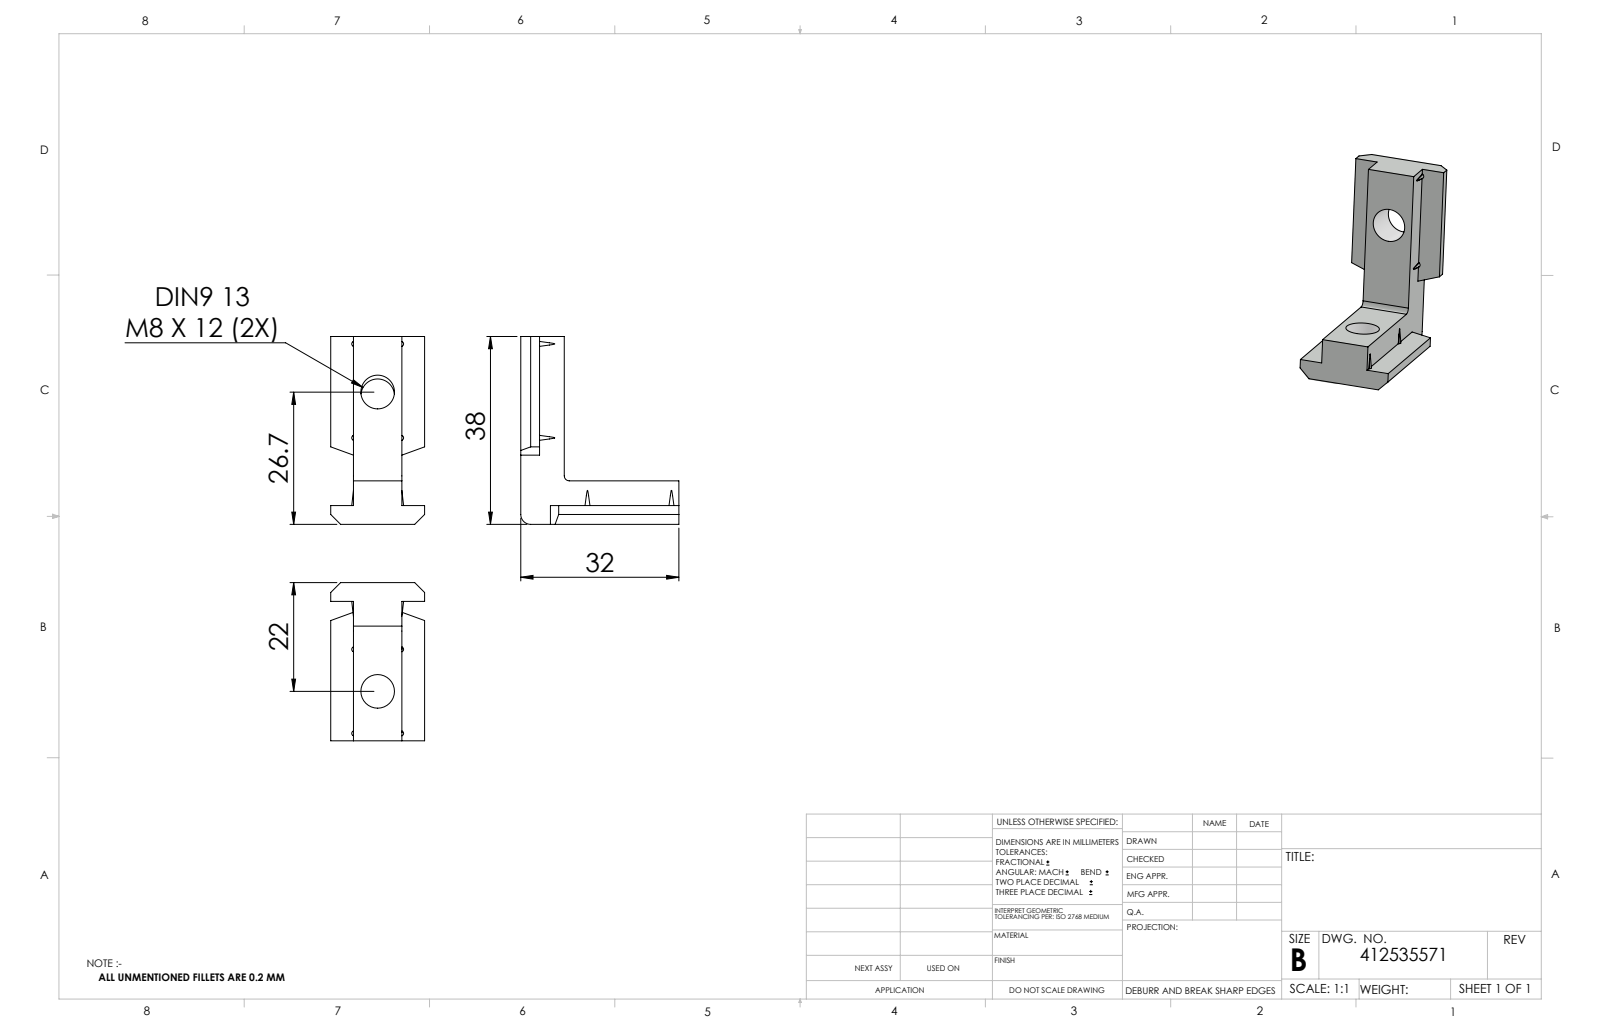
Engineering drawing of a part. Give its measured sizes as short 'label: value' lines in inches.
name: Syskomp 412535571 Innenwinkel R10_10; 412535571_c_1
written by: SolidWorks 2014 (CONFIG_CONTROL_DESIGN)
unit: in
bodies: 0 solids, 60 faces (44 planar, 6 cylindrical, 10 other)
size: 1.496 × 1.26 × 0.748
holes: 2× ⌀0.268
rounds: 1× R0.039, 1× R0.079
face distances: 0.15, 0.346, 0.197, 0.386, 0.181, 0.567, 1.26, 1.11, 0.913, 1.496
